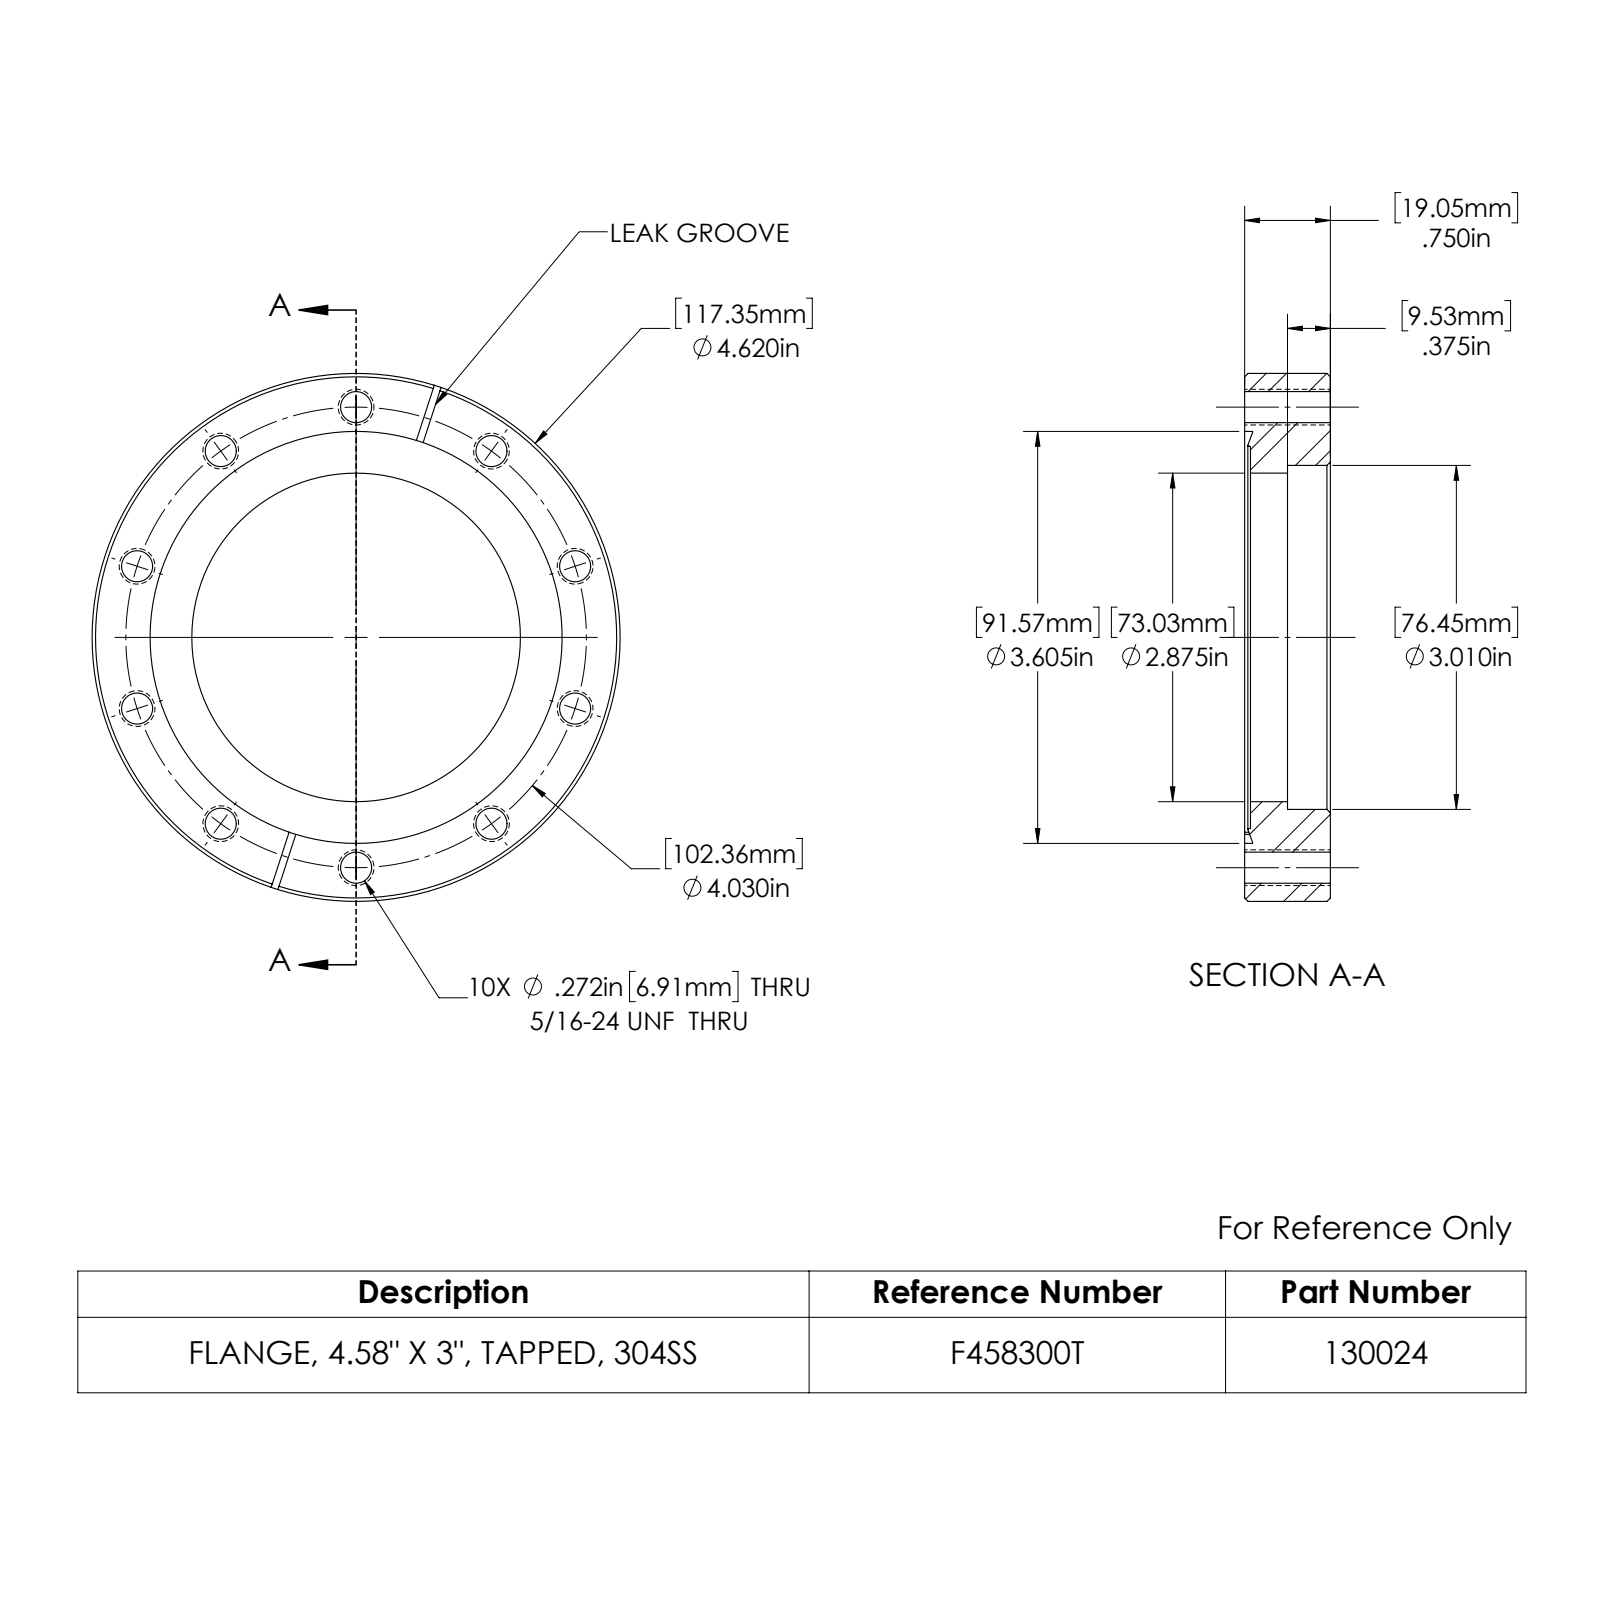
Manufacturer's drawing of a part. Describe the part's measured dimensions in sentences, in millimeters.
The part is named "130024". Its 3-D file was written by "SolidWorks 2022 (AUTOMOTIVE_DESIGN)". It is 1 solid with 58 faces: 11 planar, 28 cylindrical and 19 other. Overall it measures 117.3 by 117.3 by 19.1 millimeters. Its volume is 111 900 cubic millimeters and its surface area 28 110 square millimeters. Round holes: 10 of diameter 6.9, 1 of diameter 73, 1 of diameter 76.5, 1 of diameter 91.6. Round bosses or shafts: 1 of diameter 117.3. The main face-to-face distances are 19.1, 1.3, 17.8, 9.5, 8.2, 9.5, 1.3, 8.2, 17.7, 1.6. The hole center spacings are 31.6, 51.2, 82.8, 97.4, 31.6, 51.2, 60.2, 60.2.
